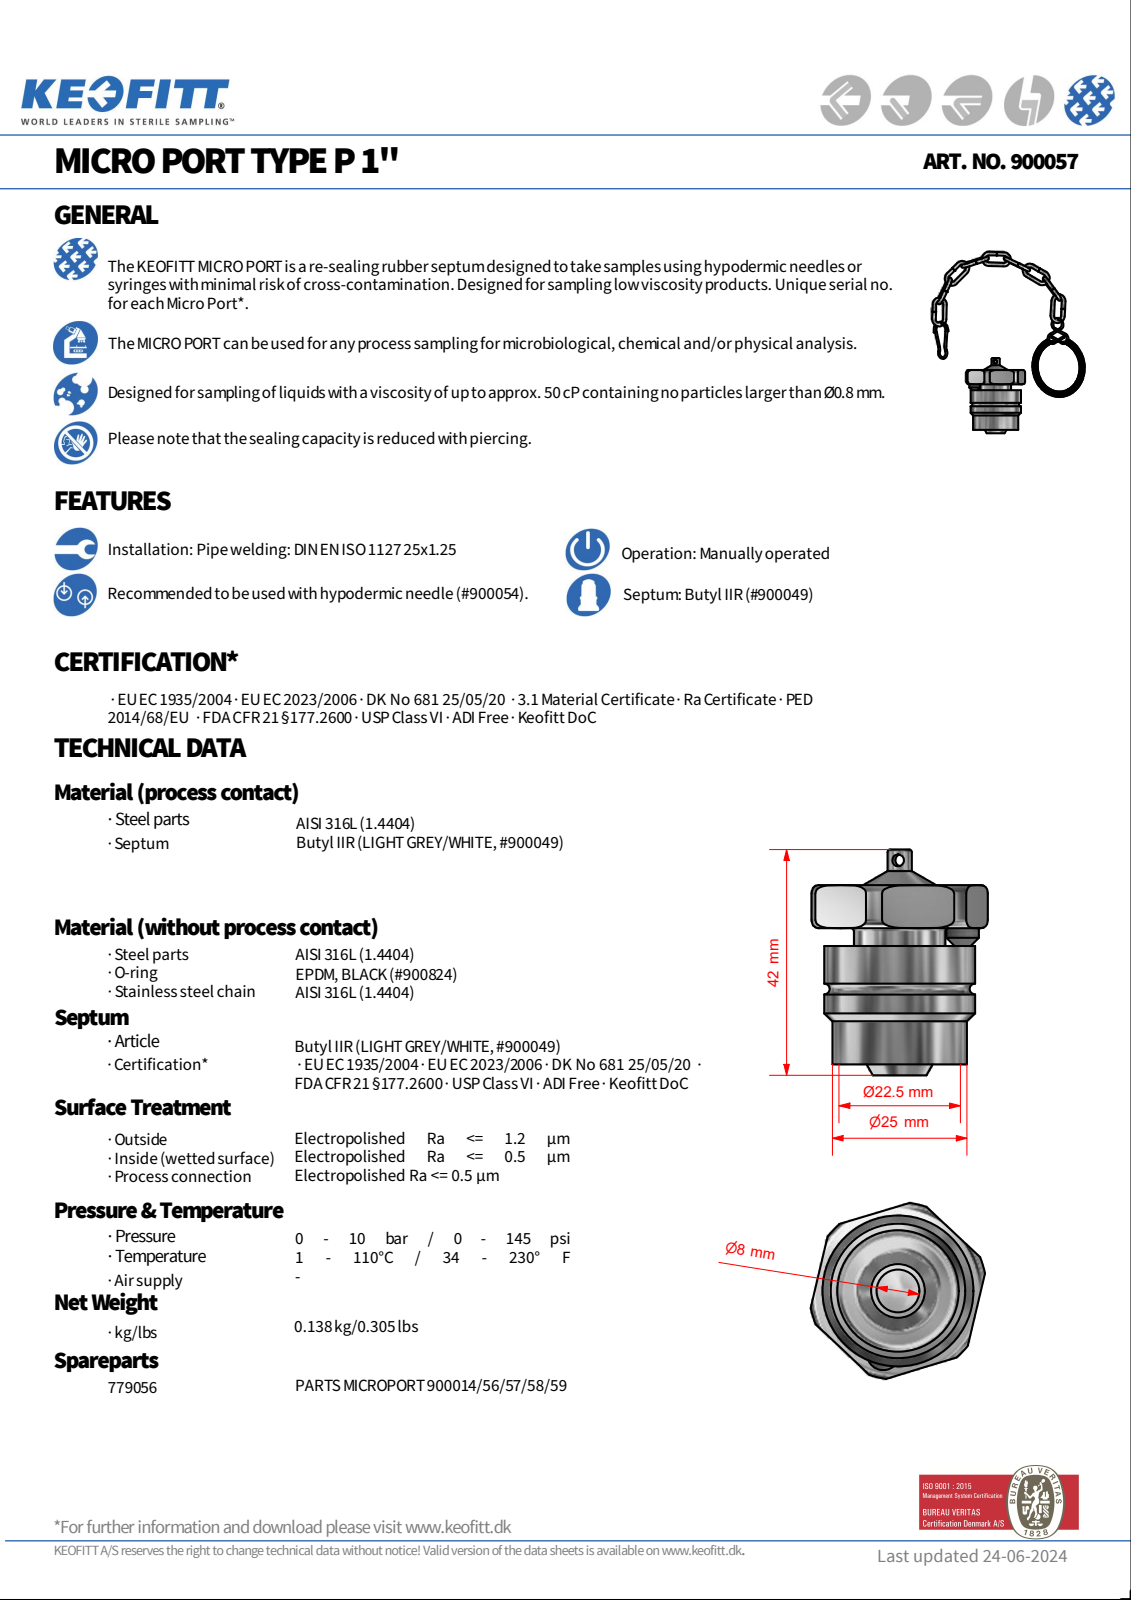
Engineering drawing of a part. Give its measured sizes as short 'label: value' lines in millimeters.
written by: Autodesk Inventor 2008 (AUTOMOTIVE_DESIGN)
unit: mm
bodies: 17 solids, 371 faces (65 planar, 70 cylindrical, 236 other)
size: 84.83 × 69.81 × 41.44
volume: 20 420 mm³; area: 9 842 mm²
holes: 9× ⌀2, 1× ⌀0.2, 1× ⌀2.2, 1× ⌀5.2, 1× ⌀8, 1× ⌀22.5
bosses: 21× ⌀2, 1× ⌀28, 1× ⌀25, 1× ⌀17, 1× ⌀14, 1× ⌀6, 1× ⌀4.5
rounds: 8× R0.1, 1× R16.5
face distances: 8, 11.3, 3.3, 2, 29.98, 29.99, 30.01, 33.3, 25.3, 22
hole spacings: 3, 12
